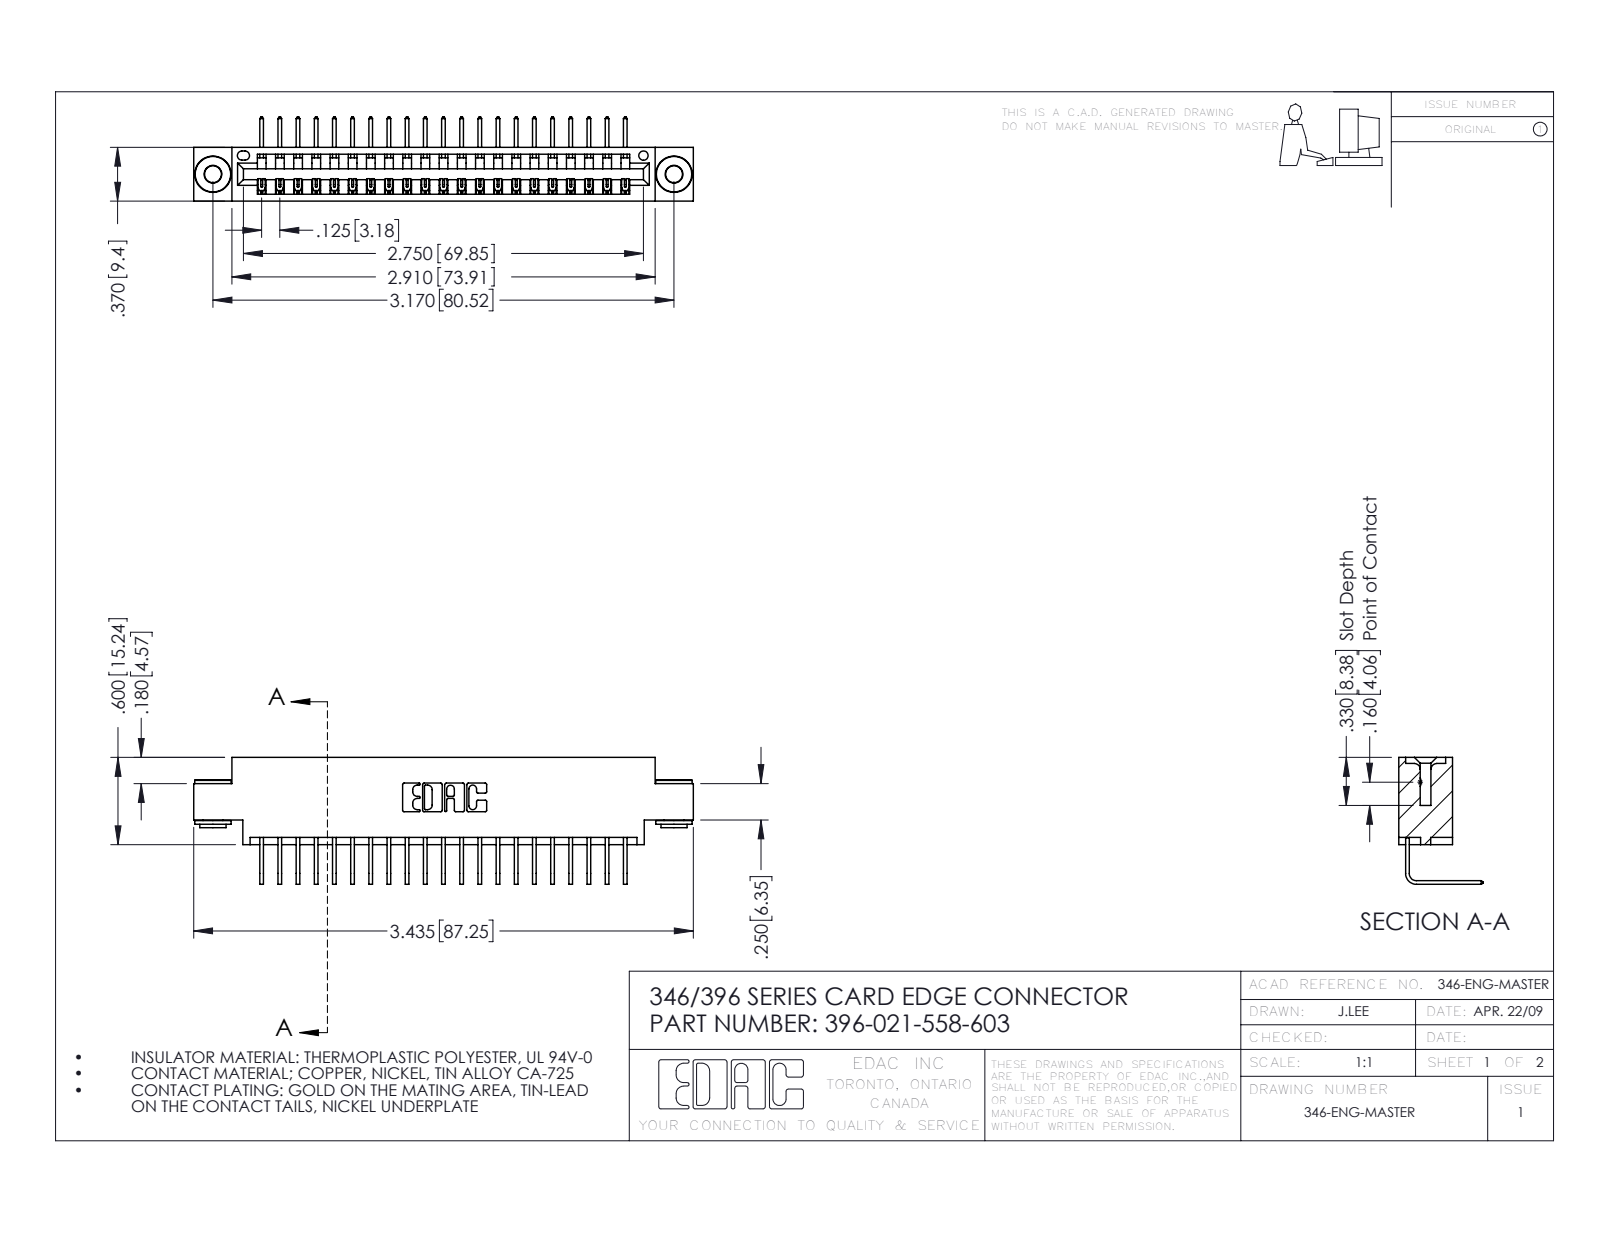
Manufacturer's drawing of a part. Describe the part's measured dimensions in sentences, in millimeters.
The part is named "345-250-002_345-250-002-102; 345-292-001_558 Tail - 2; 346 Part_0.170 Offset - 0.156 Dia-TH; 396-021-558-603". Its 3-D file was written by "SolidWorks 2016 (CONFIG_CONTROL_DESIGN)". It is 24 solids with 1424 faces: 972 planar, 444 cylindrical and 8 other. Overall it measures 87.2 by 22.2 by 14.7 millimeters. Its volume is 8 140 cubic millimeters and its surface area 10 750 square millimeters. Round holes: 2 of diameter 2.9, 2 of diameter 4, 1 of diameter 1.6. Round bosses or shafts: 2 of diameter 6.4, 2 of diameter 4.6, 2 of diameter 3.5. Partial cylindrical surfaces (rounded edges, fillets, slot ends): 42 of radius 0.2, 22 of radius 0.3, 6 of radius 0.2, 6 of radius 0.8, 3 of radius 0.7, 2 of radius 0.8, 2 of radius 1, 1 of radius 0.4. The main face-to-face distances are 8.2, 1.2, 9.4, 6.4, 0.6, 7.6, 1.8, 3.8, 5.6, 2.5. The hole center spacings are 6.2, 75.3, 80.5.
